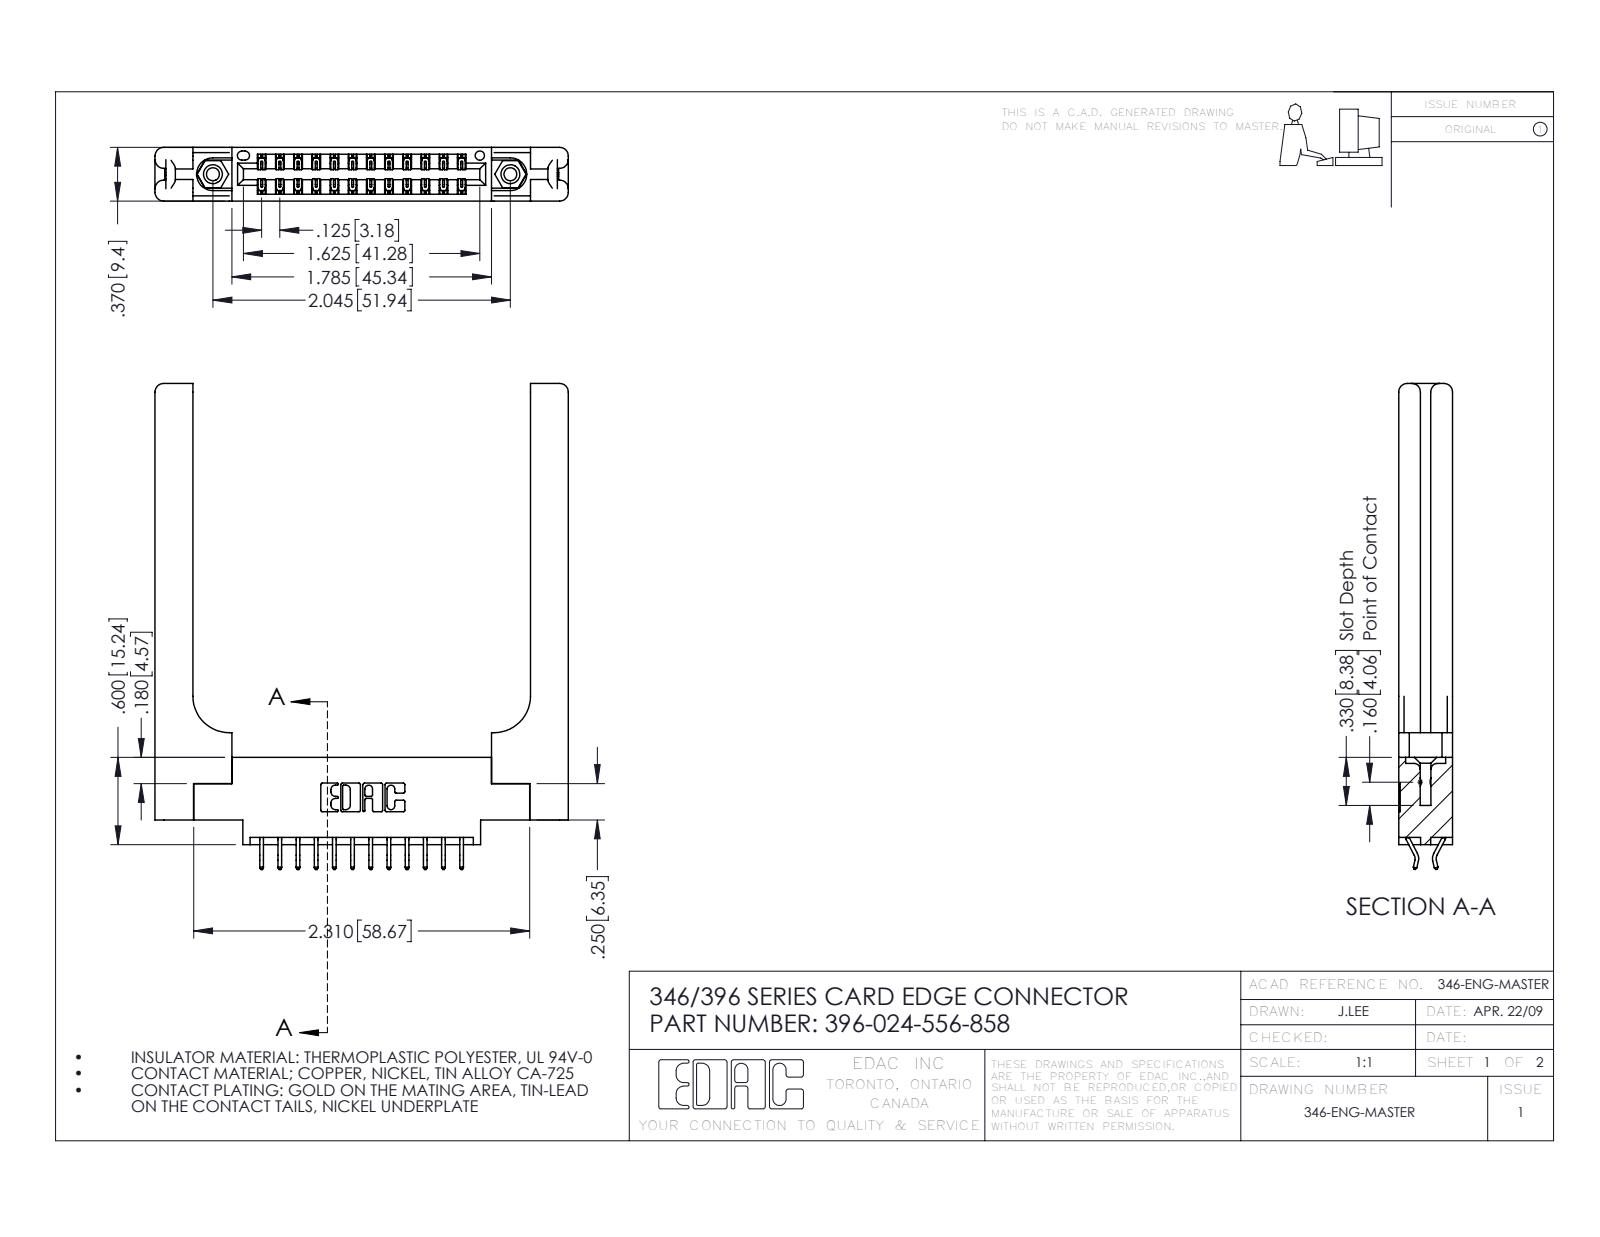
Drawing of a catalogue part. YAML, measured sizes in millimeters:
part_name: "346-220-058_345-220-058; 396-024-556-858; 346 Part_0.170 Offset - 0.156 Dia-TH; 345-250-001_345-250-001-102 (+1 more)"
step_written_by: "SolidWorks 2016 (CONFIG_CONTROL_DESIGN)"
units: millimeters
bodies: {solids: 29, faces: 1774, planar: 1164, cylindrical: 550, other: 60}
overall_size: [84.8, 72.2, 9.4]
volume: 14100
surface_area: 13800
round_holes:
  - {diameter: 2.3, count: 2}
  - {diameter: 3.2, count: 2}
  - {diameter: 4, count: 2}
  - {diameter: 1.6, count: 1}
round_bosses_or_shafts:
  - {diameter: 3.9, count: 2}
partial_cylinders:
  - {radius: 0.2, count: 36}
  - {radius: 0.3, count: 22}
  - {radius: 1.5, count: 16}
  - {radius: 0.2, count: 6}
  - {radius: 0.8, count: 6}
  - {radius: 0.7, count: 3}
  - {radius: 0.3, count: 2}
  - {radius: 0.4, count: 2}
face_to_face_distances: [9.4, 3.8, 1.8, 3.8, 1.2, 8.2, 2.6, 5.6, 4.4, 6.4]
hole_center_spacings: [6.2, 46.7, 51.9]
